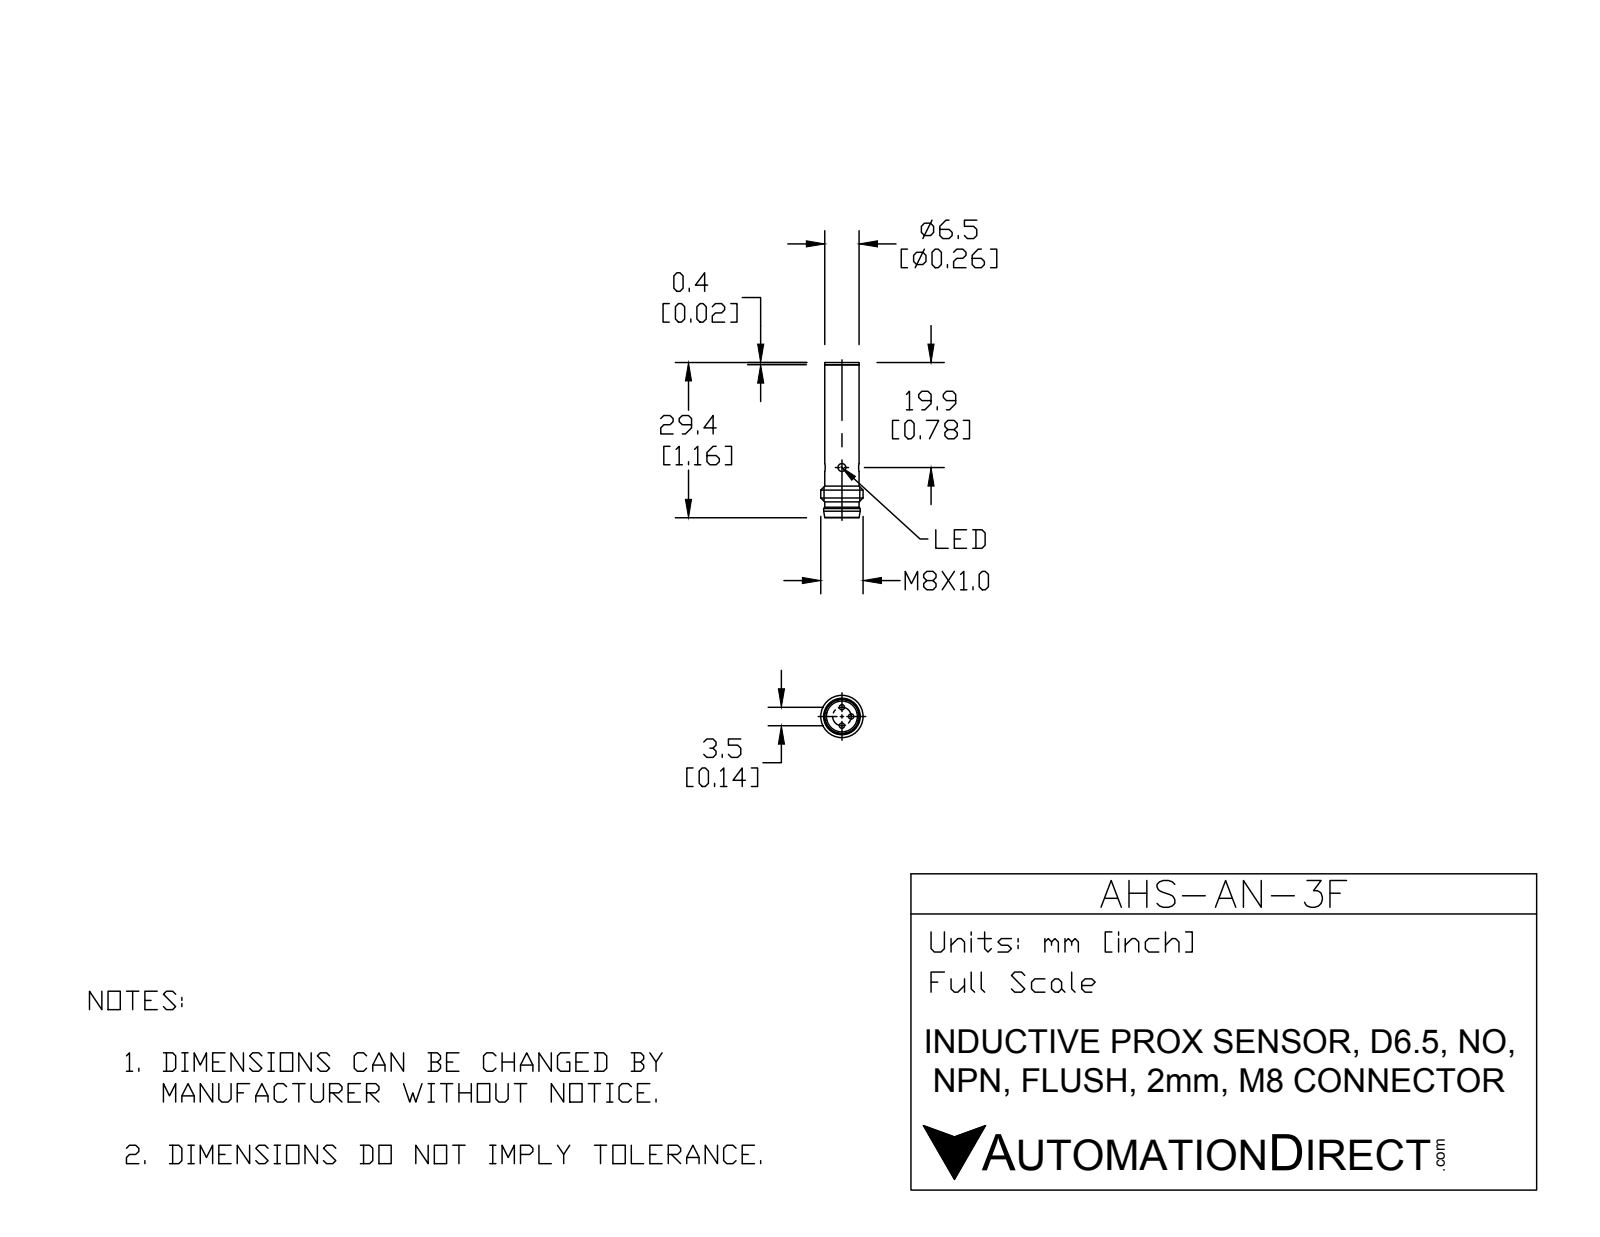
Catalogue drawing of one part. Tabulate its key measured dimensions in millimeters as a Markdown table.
| quantity | value |
| --- | --- |
| part name | AHS-AN-3F |
| STEP written by | SolidWorks 2015 (CONFIG_CONTROL_DESIGN) |
| units | millimeters |
| bodies | 4 solids, 56 faces (12 planar, 26 cylindrical, 18 other) |
| overall size | 29.4 × 8 × 8 |
| volume | 891 mm³ |
| surface area | 842 mm² |
| round holes (diameter × count) | 1.5 × 2, 5.85 × 1 |
| round bosses / shafts (diameter × count) | 1 × 3, 8 × 1, 6.9 × 1, 6.5 × 1 |
| main face-to-face distances | 24.4, 3, 27.4, 5.5, 2, 5, 29.4, 29, 27, 24 |
